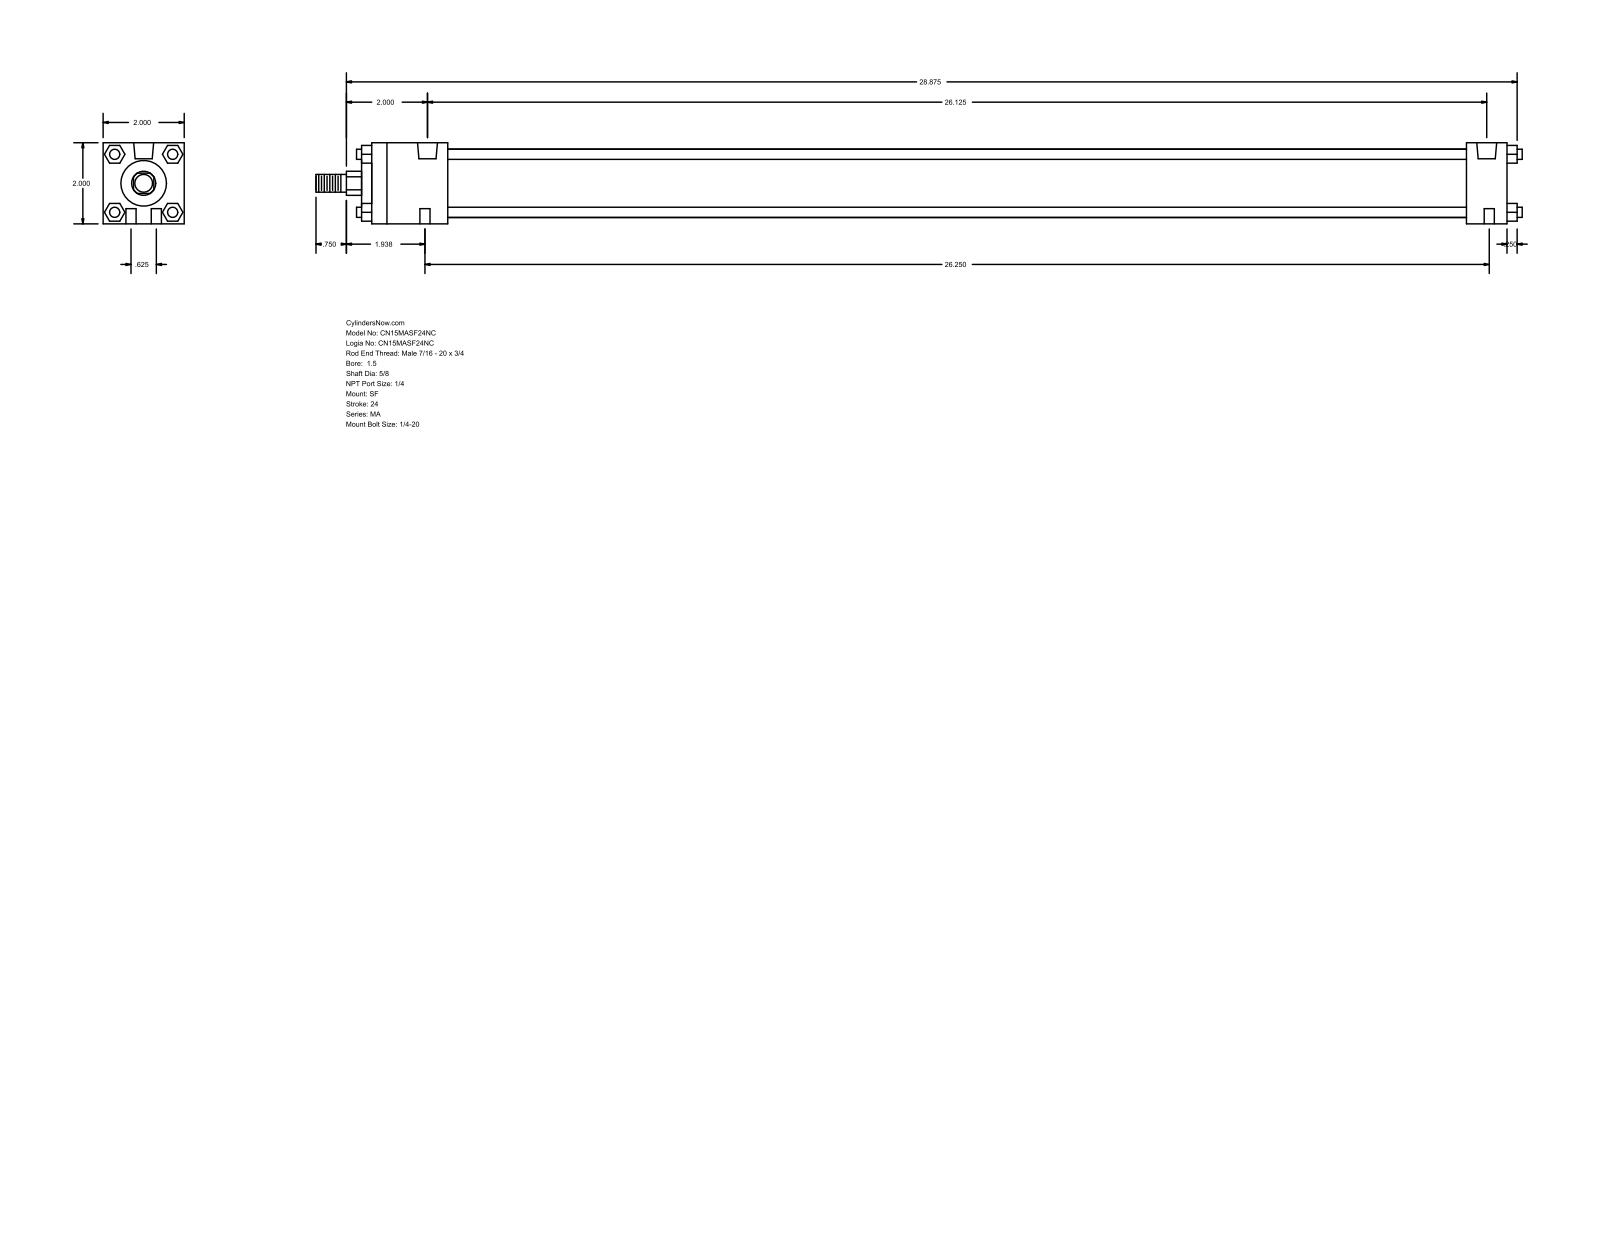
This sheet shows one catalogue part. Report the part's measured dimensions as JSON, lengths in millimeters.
{"part_name": "MA_SF__0150_0.625", "step_written_by": "GSSL Pune (CONFIG_CONTROL_DESIGN)", "units": "millimeters", "bodies": {"solids": 0, "faces": 124, "planar": 94, "cylindrical": 30, "other": 0}, "overall_size": [755.65, 50.8, 50.8], "round_holes": [[6.35, 4], [7.94, 2], [12.49, 2]], "round_bosses_or_shafts": [[6.35, 4], [42.93, 1], [28.57, 1], [15.88, 1], [11.11, 1]], "partial_cylinders_radius": [[7.54, 1]], "face_to_face_distances": [50.8, 711.2, 47.62, 685.79, 638.17, 663.58, 25.41, 6.35, 53.97, 692.14], "hole_center_spacings": [8.1, 15.88, 663.58, 665.21, 665.22, 666.75, 666.94]}
